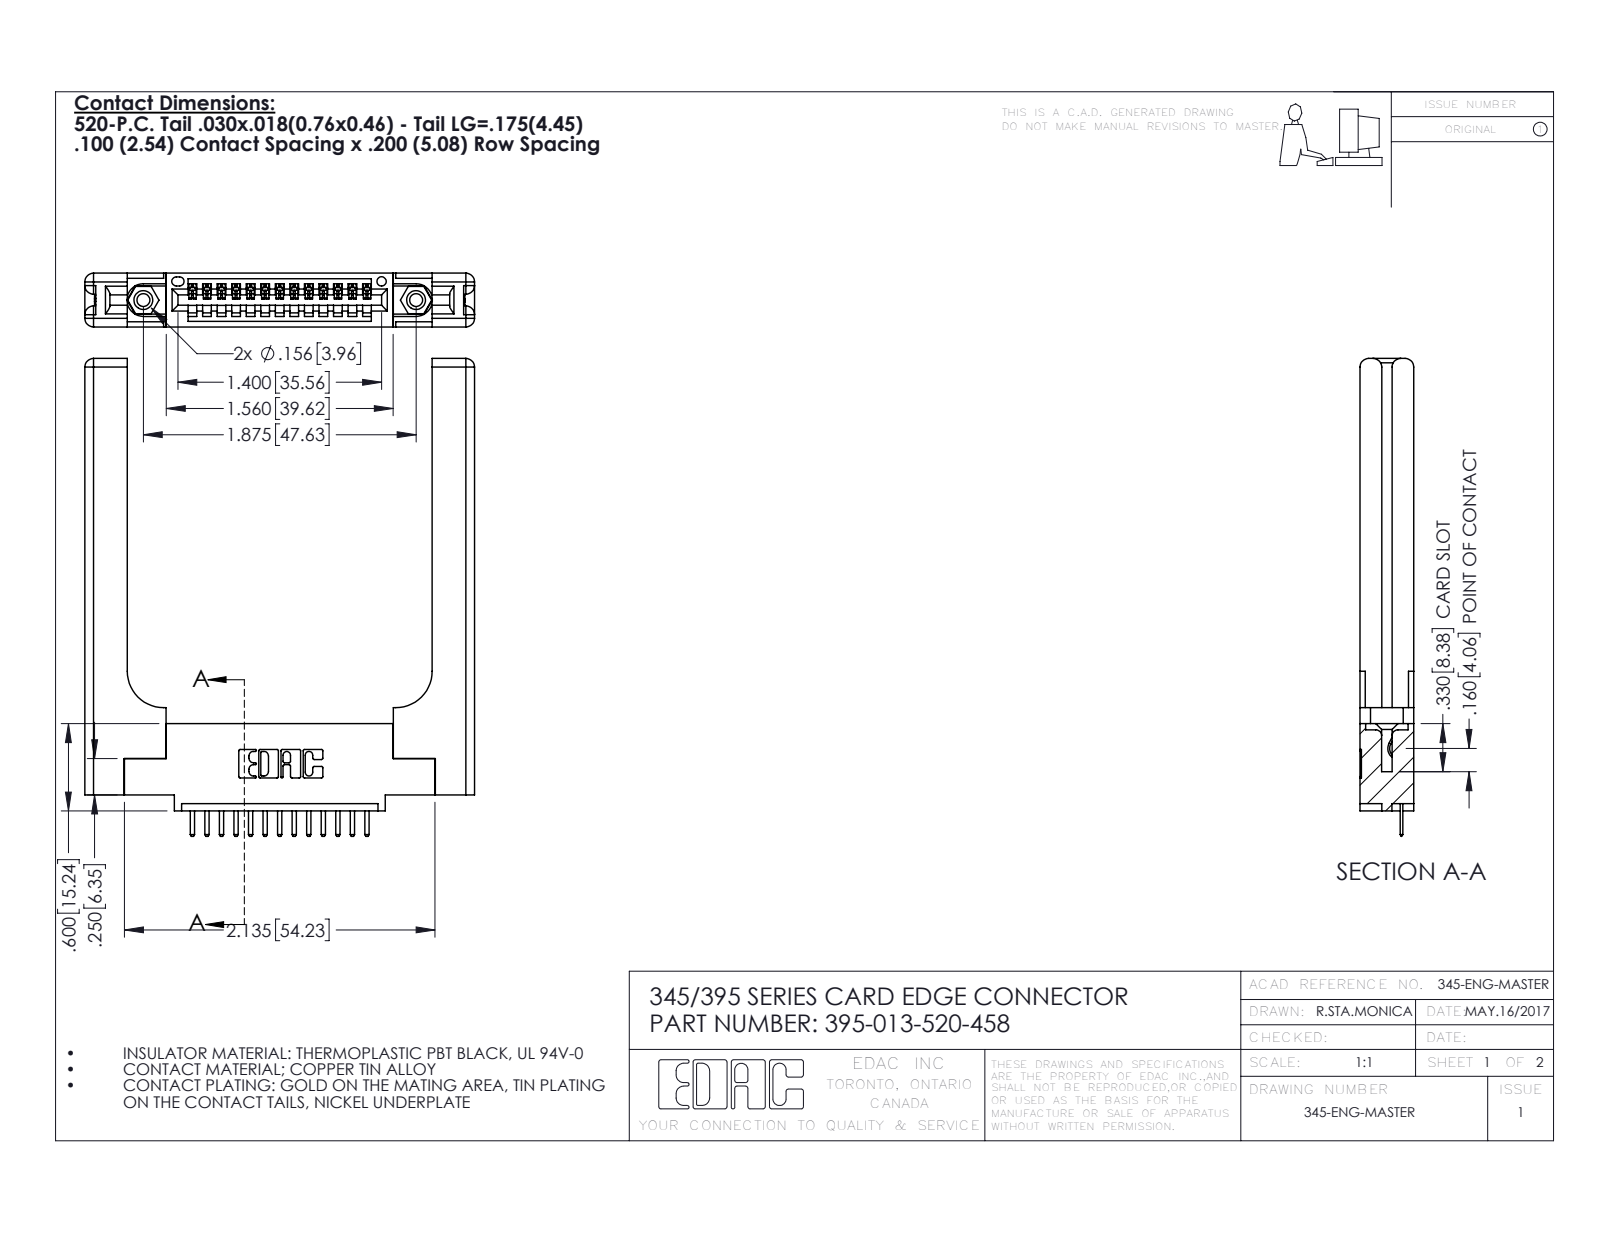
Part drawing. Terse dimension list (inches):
name: 345-292-001_345-293-120; 395-013-520-458; 345 Part_0.110 Offset - 0.156 Dia-TH; 345-220-058_345-220-058 (+1 more)
written by: SolidWorks 2016 (CONFIG_CONTROL_DESIGN)
unit: in
bodies: 18 solids, 1192 faces (778 planar, 354 cylindrical, 60 other)
size: 3.285 × 2.679 × 0.37
volume: 0.892 in³; area: 20.15 in²
holes: 2× ⌀0.089, 2× ⌀0.125, 2× ⌀0.156, 1× ⌀0.064
bosses: 2× ⌀0.155
rounds: 28× R0.01, 26× R0.006, 22× R0.01, 16× R0.06, 6× R0.007, 6× R0.031, 3× R0.026, 2× R0.03
face distances: 0.37, 0.072, 0.15, 0.148, 0.077, 0.22, 0.298, 2.096, 0.071, 0.225
hole spacings: 0.27, 1.643, 1.875
